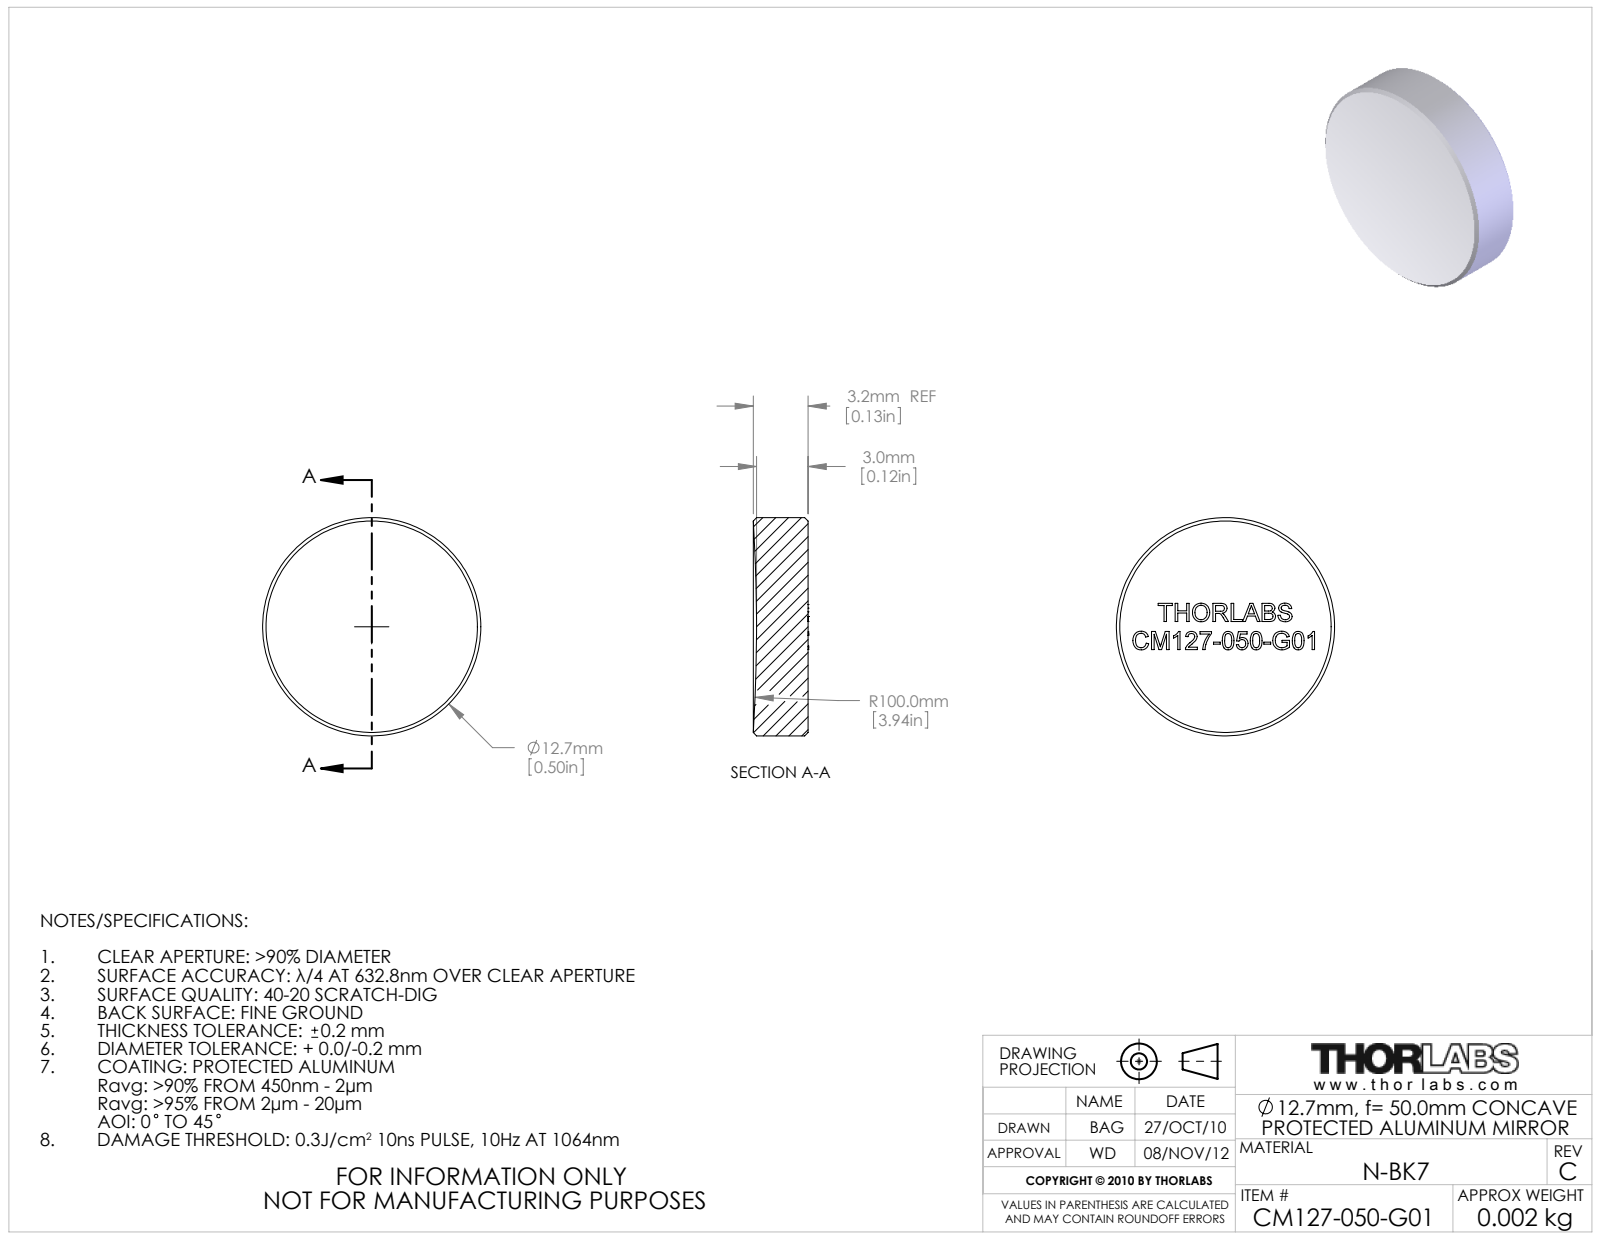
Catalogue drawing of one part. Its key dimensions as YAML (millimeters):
part_name: "12008-E0W"
step_written_by: "SolidWorks 2009 (AUTOMOTIVE_DESIGN)"
units: millimeters
bodies: {solids: 1, faces: 268, planar: 144, cylindrical: 2, other: 122}
overall_size: [12.7, 12.7, 3.2]
volume: 390
surface_area: 372
round_bosses_or_shafts:
  - {diameter: 12.7, count: 1}
face_to_face_distances: [1.1, 1.3, 0.9, 0.7, 0.9, 0.7, 1.2, 0.5, 1.2, 1]
